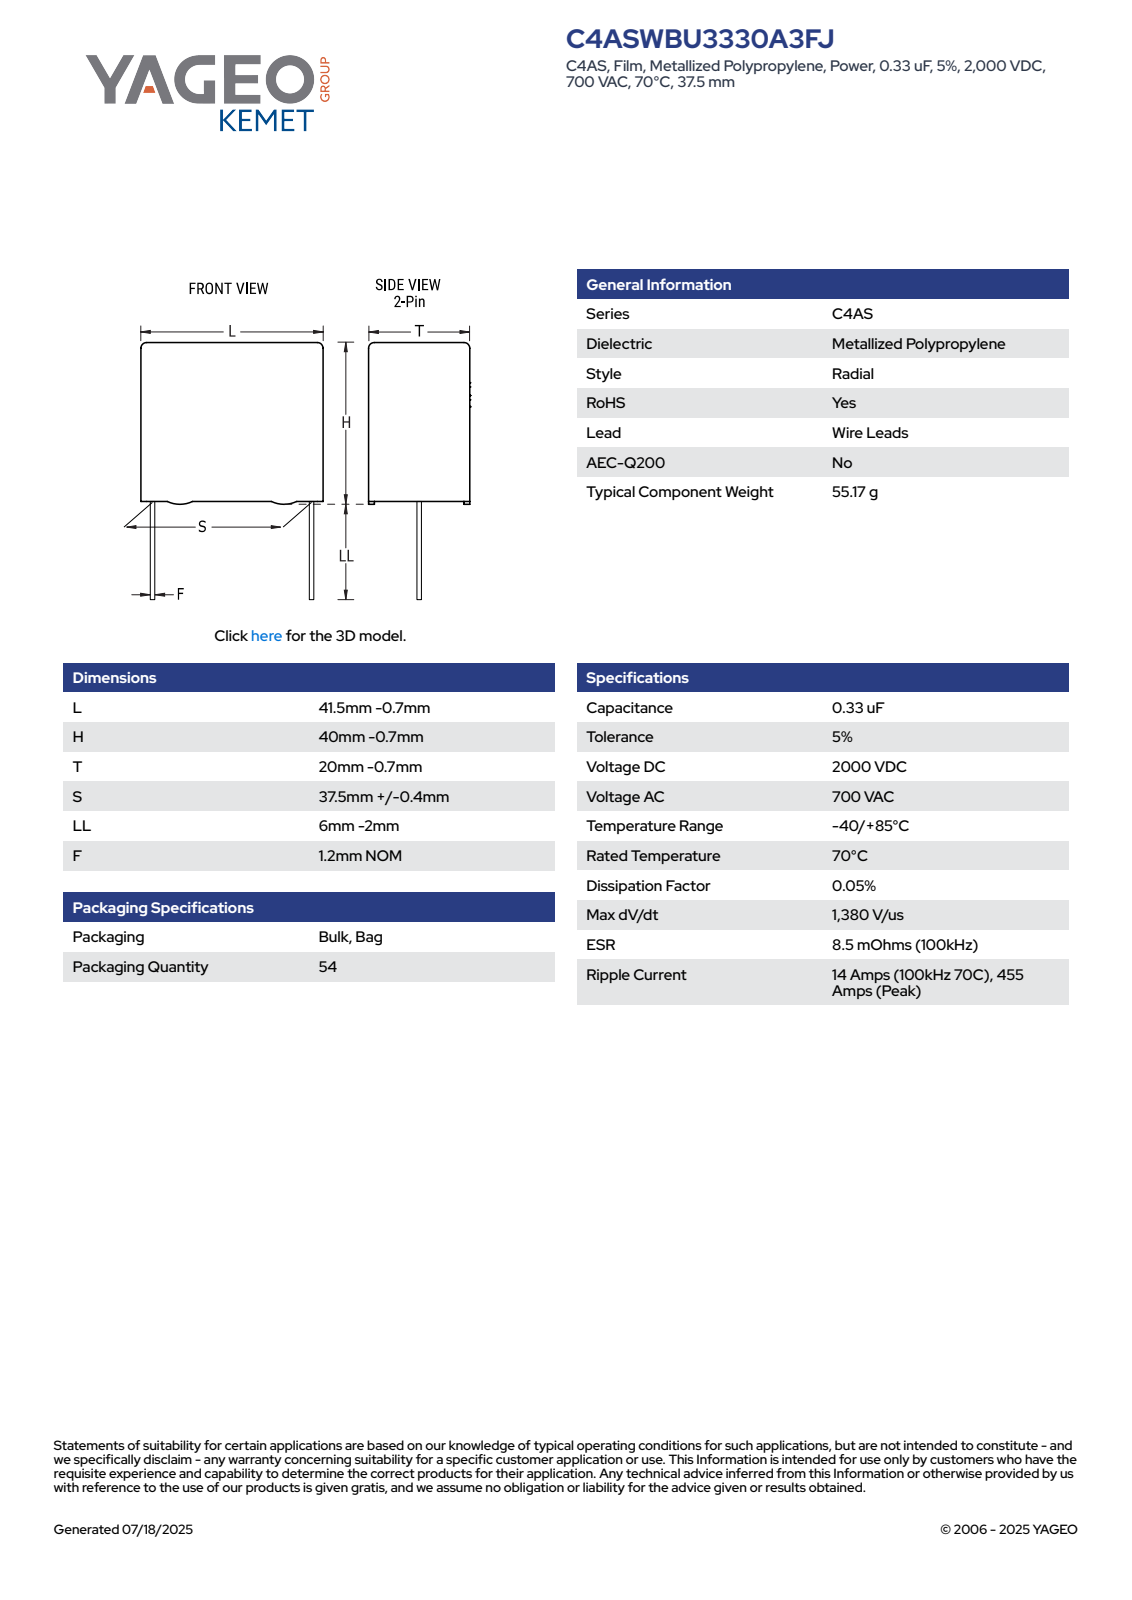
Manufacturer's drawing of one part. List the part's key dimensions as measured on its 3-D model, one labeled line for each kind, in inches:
Part name (STEP PRODUCT): CFP_RB_41.5X40X20_L40.8H39.3T19.3S37.5LL4F1.2
STEP written by: SolidWorks 2014 (AUTOMOTIVE_DESIGN)
Units: inches
Bodies: 4 solids, 89 faces (81 planar, 8 cylindrical, 0 other)
Overall size (bounding box): 1.705 × 1.606 × 0.76
Volume: 1.852 in³ · Surface area: 9.816 in²
Round bosses / shafts (diameter × count): ⌀0.047 ×2
Partial cylindrical surfaces — rounded edges, fillets, slot ends (radius × count): R0.02 ×4
Main face-to-face distances: 0.76, 1.606, 1.516, 0.031, 1.547, 0.76, 0.043, 0.717, 0.044, 0.673
